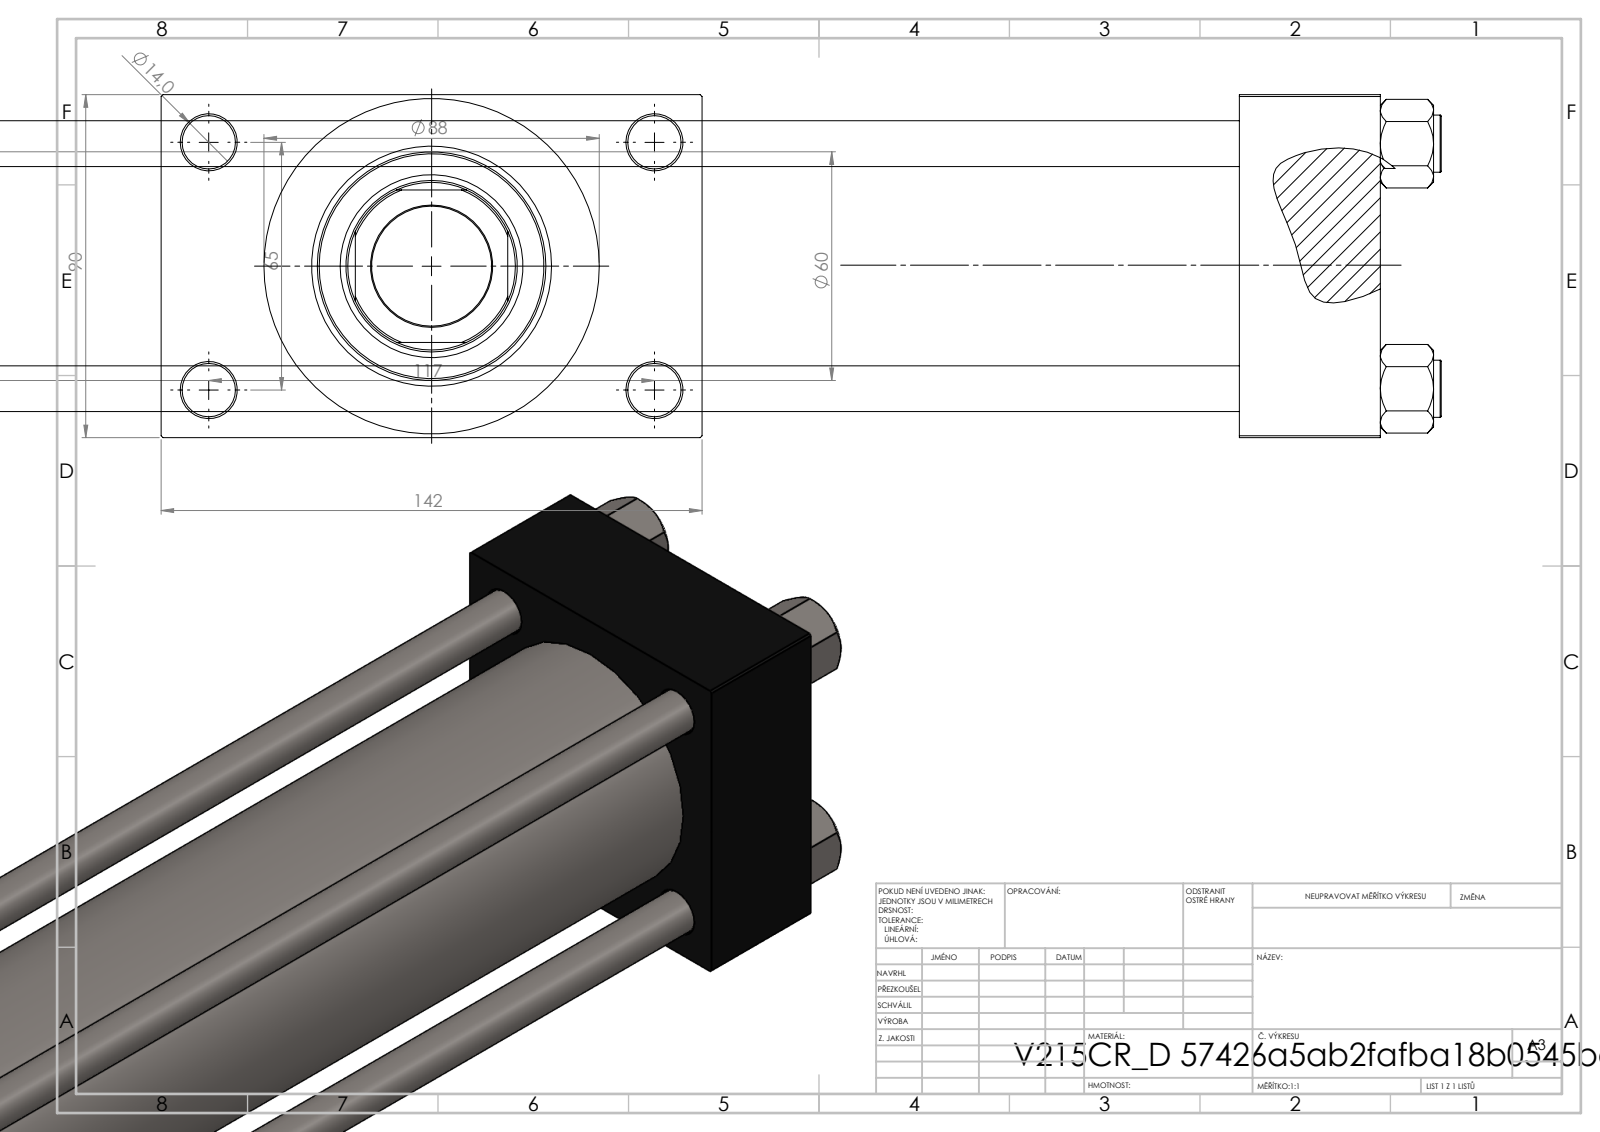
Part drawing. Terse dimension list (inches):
name: V215CR_VCP_D; V215CR_D_Body; V215CR_D_TYCINKA; V215_VC_A (+1 more)
written by: SolidWorks 2019 (CONFIG_CONTROL_DESIGN)
unit: in
bodies: 11 solids, 1102 faces (496 planar, 86 cylindrical, 520 other)
size: 20.984 × 5.591 × 3.543
volume: 124.4 in³; area: 690.8 in²
holes: 4× ⌀0.472, 4× ⌀0.551, 2× ⌀0.276, 2× ⌀0.825, 2× ⌀1.181, 1× ⌀1.24, 1× ⌀1.772, 1× ⌀1.89, 1× ⌀1.969, 1× ⌀2.362, 1× ⌀2.48
bosses: 4× ⌀0.591, 1× ⌀3.465, 1× ⌀2.717
rounds: 1× R0.866
face distances: 3.543, 15.315, 1.457, 16.772, 1.024, 18.504, 17.047, 1.732, 4.567, 2.362
hole spacings: 1.037, 1.79, 2.531, 2.635, 2.748, 3.569, 4.383, 2.559
